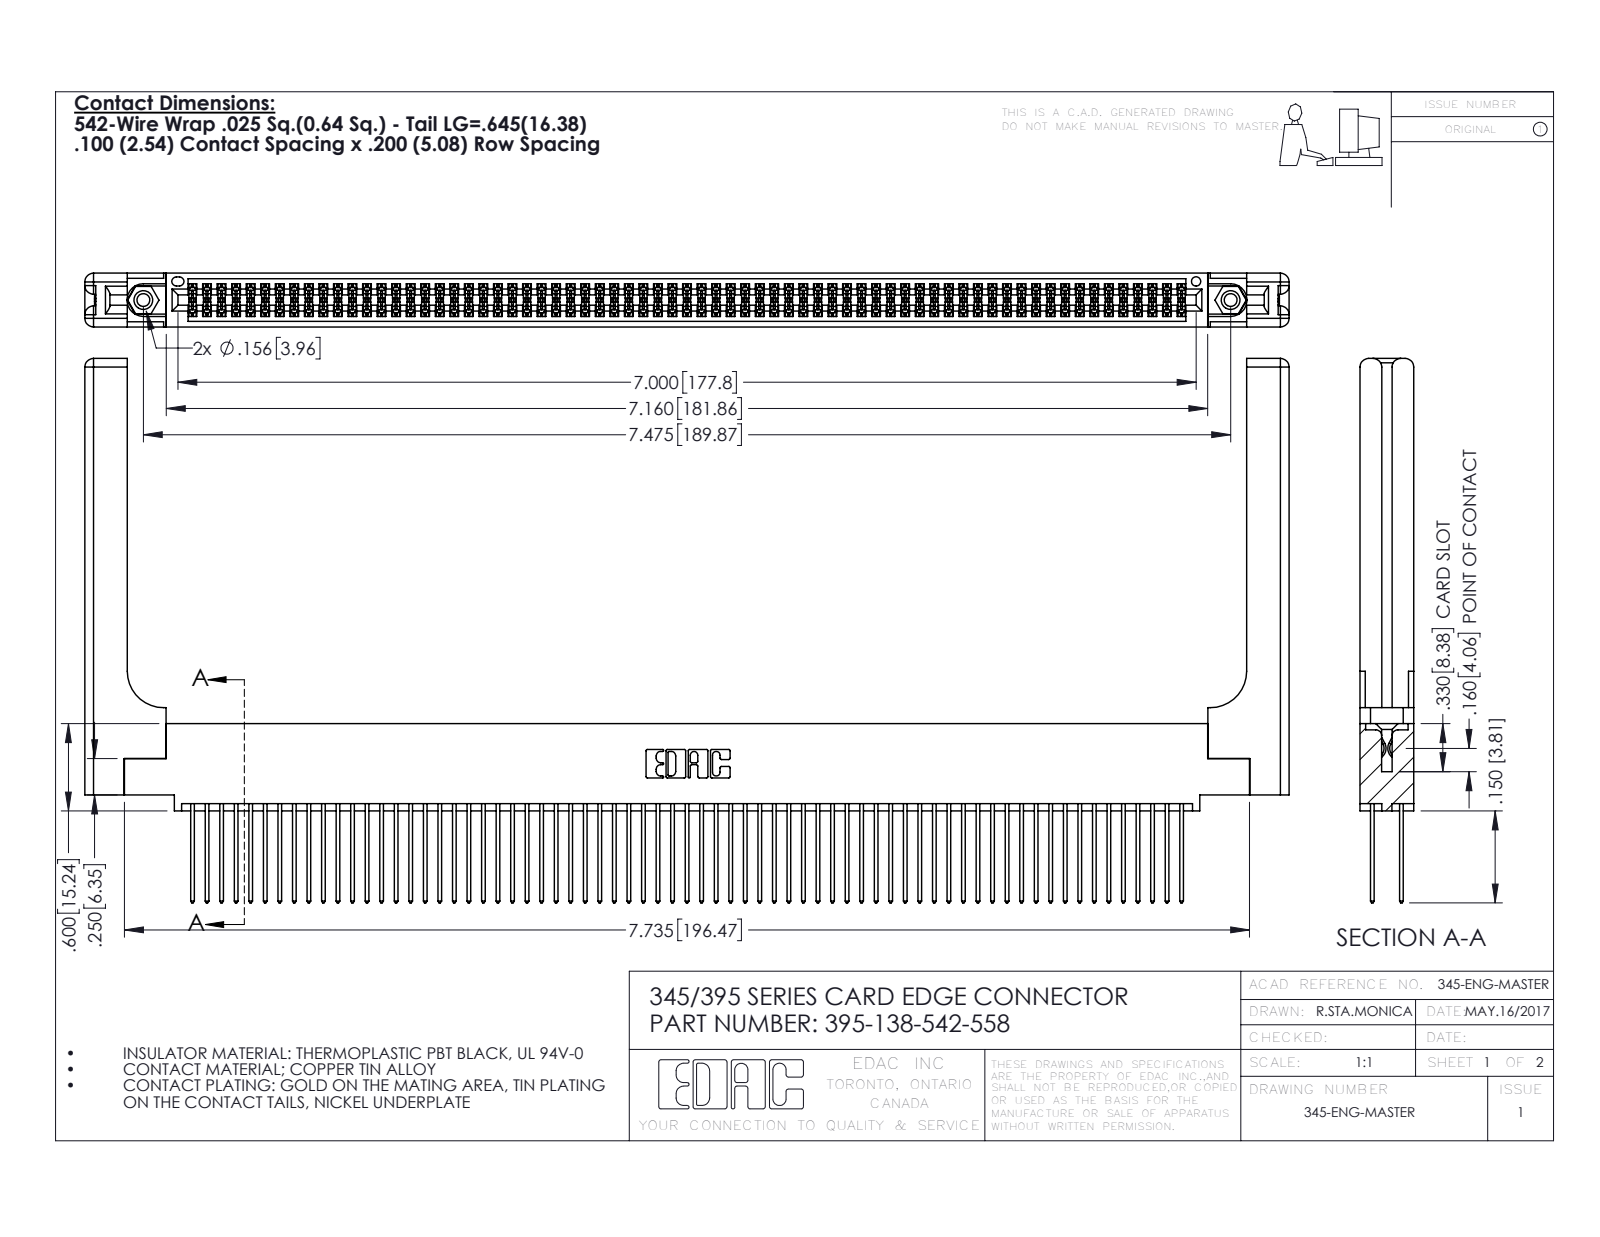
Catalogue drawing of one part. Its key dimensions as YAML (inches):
part_name: "345-220-058_345-220-058; 345-250-001_345-250-001-102; 395-138-542-558; 345 Part_0.110 Offset - 0.156 Dia-TH (+1 more)"
step_written_by: "SolidWorks 2016 (CONFIG_CONTROL_DESIGN)"
units: inches
bodies: {solids: 143, faces: 7286, planar: 4786, cylindrical: 2440, other: 60}
overall_size: [8.279, 3.742, 0.37]
volume: 1.814
surface_area: 62.14
round_holes:
  - {diameter: 0.089, count: 2}
  - {diameter: 0.125, count: 2}
  - {diameter: 0.156, count: 2}
  - {diameter: 0.064, count: 1}
round_bosses_or_shafts:
  - {diameter: 0.155, count: 2}
partial_cylinders:
  - {radius: 0.006, count: 207}
  - {radius: 0.01, count: 138}
  - {radius: 0.01, count: 22}
  - {radius: 0.06, count: 16}
  - {radius: 0.007, count: 6}
  - {radius: 0.031, count: 6}
  - {radius: 0.026, count: 3}
  - {radius: 0.014, count: 2}
face_to_face_distances: [0.072, 0.298, 0.098, 0.272, 0.025, 0.2, 0.37, 0.225, 0.175, 0.148]
hole_center_spacings: [0.27, 7.239, 7.475]
